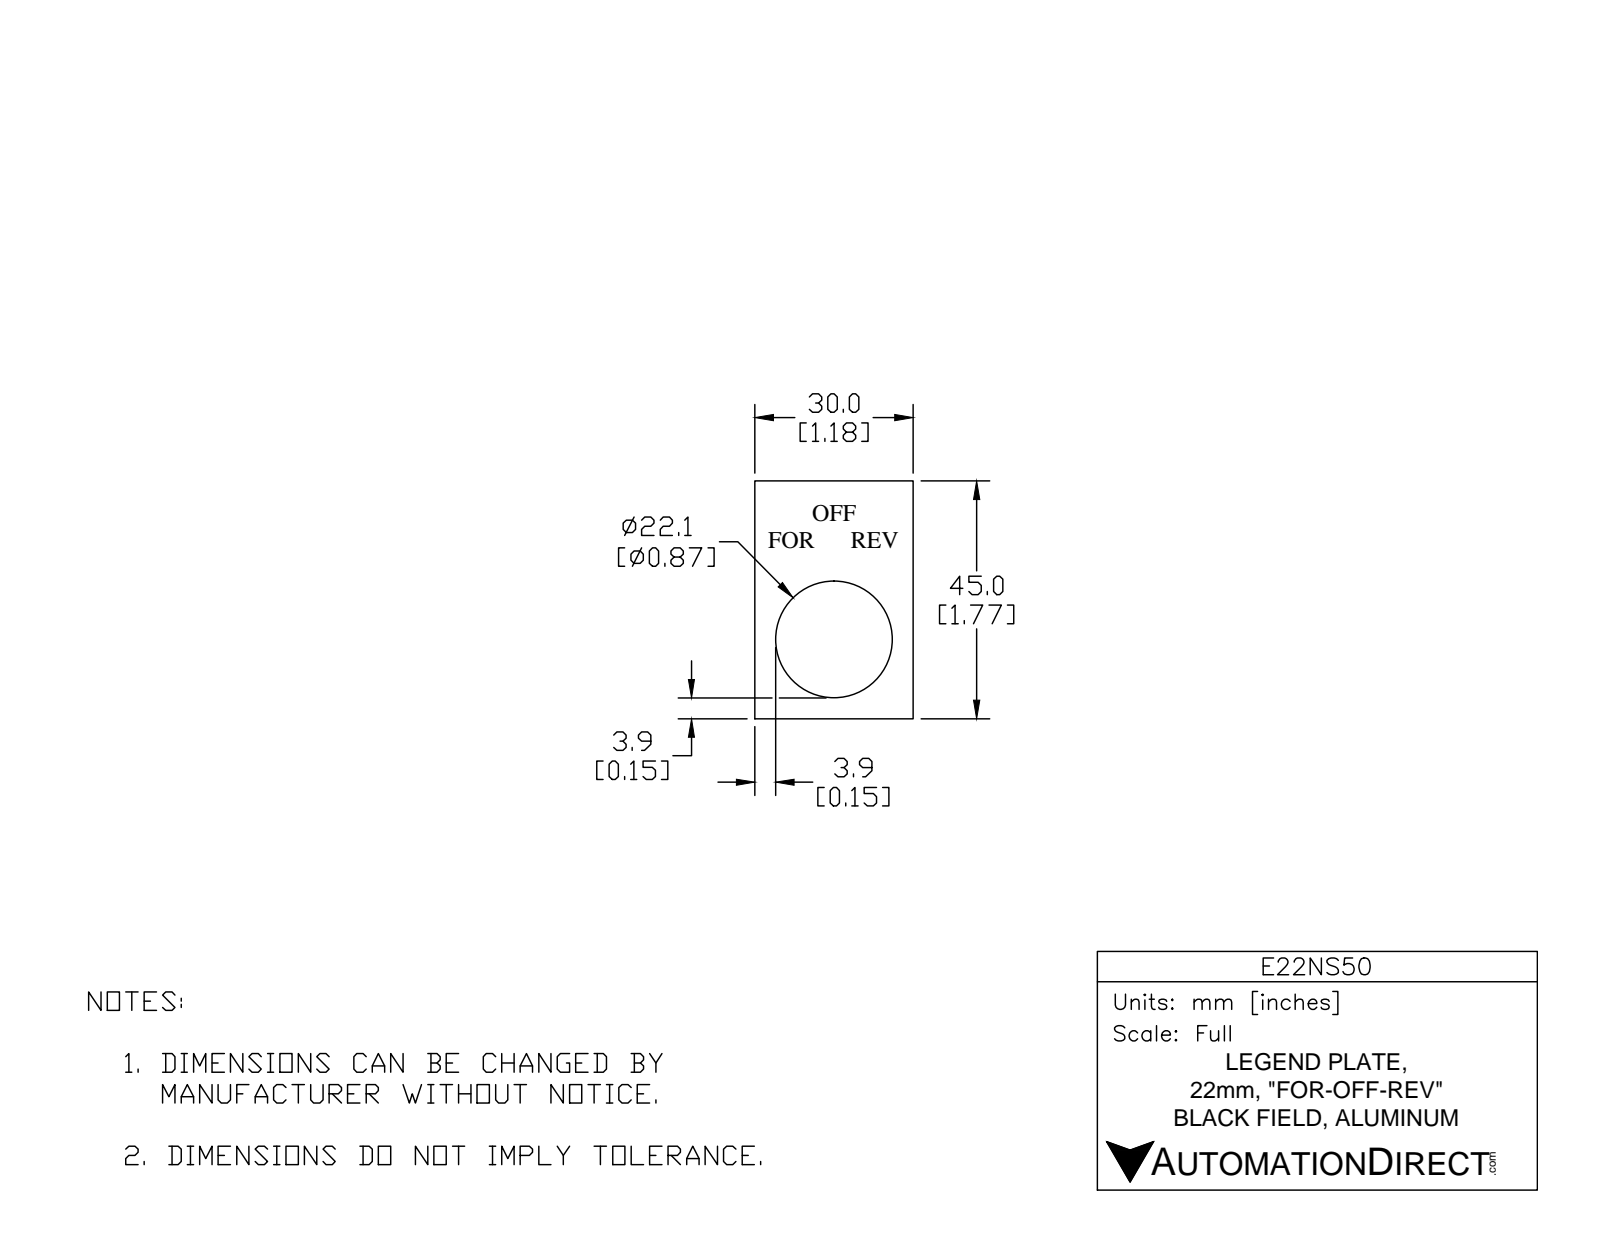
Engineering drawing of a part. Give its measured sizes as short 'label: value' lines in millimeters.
name: E22NS50
written by: SolidWorks 2017 (AUTOMOTIVE_DESIGN)
unit: mm
bodies: 1 solid, 132 faces (103 planar, 3 cylindrical, 26 other)
size: 45 × 30 × 1.3
volume: 1 250 mm³; area: 2 254 mm²
holes: 1× ⌀22.2
face distances: 1.3, 30, 45, 1.05, 4.7, 40.3, 0.32, 13.4, 0.98, 38.17
